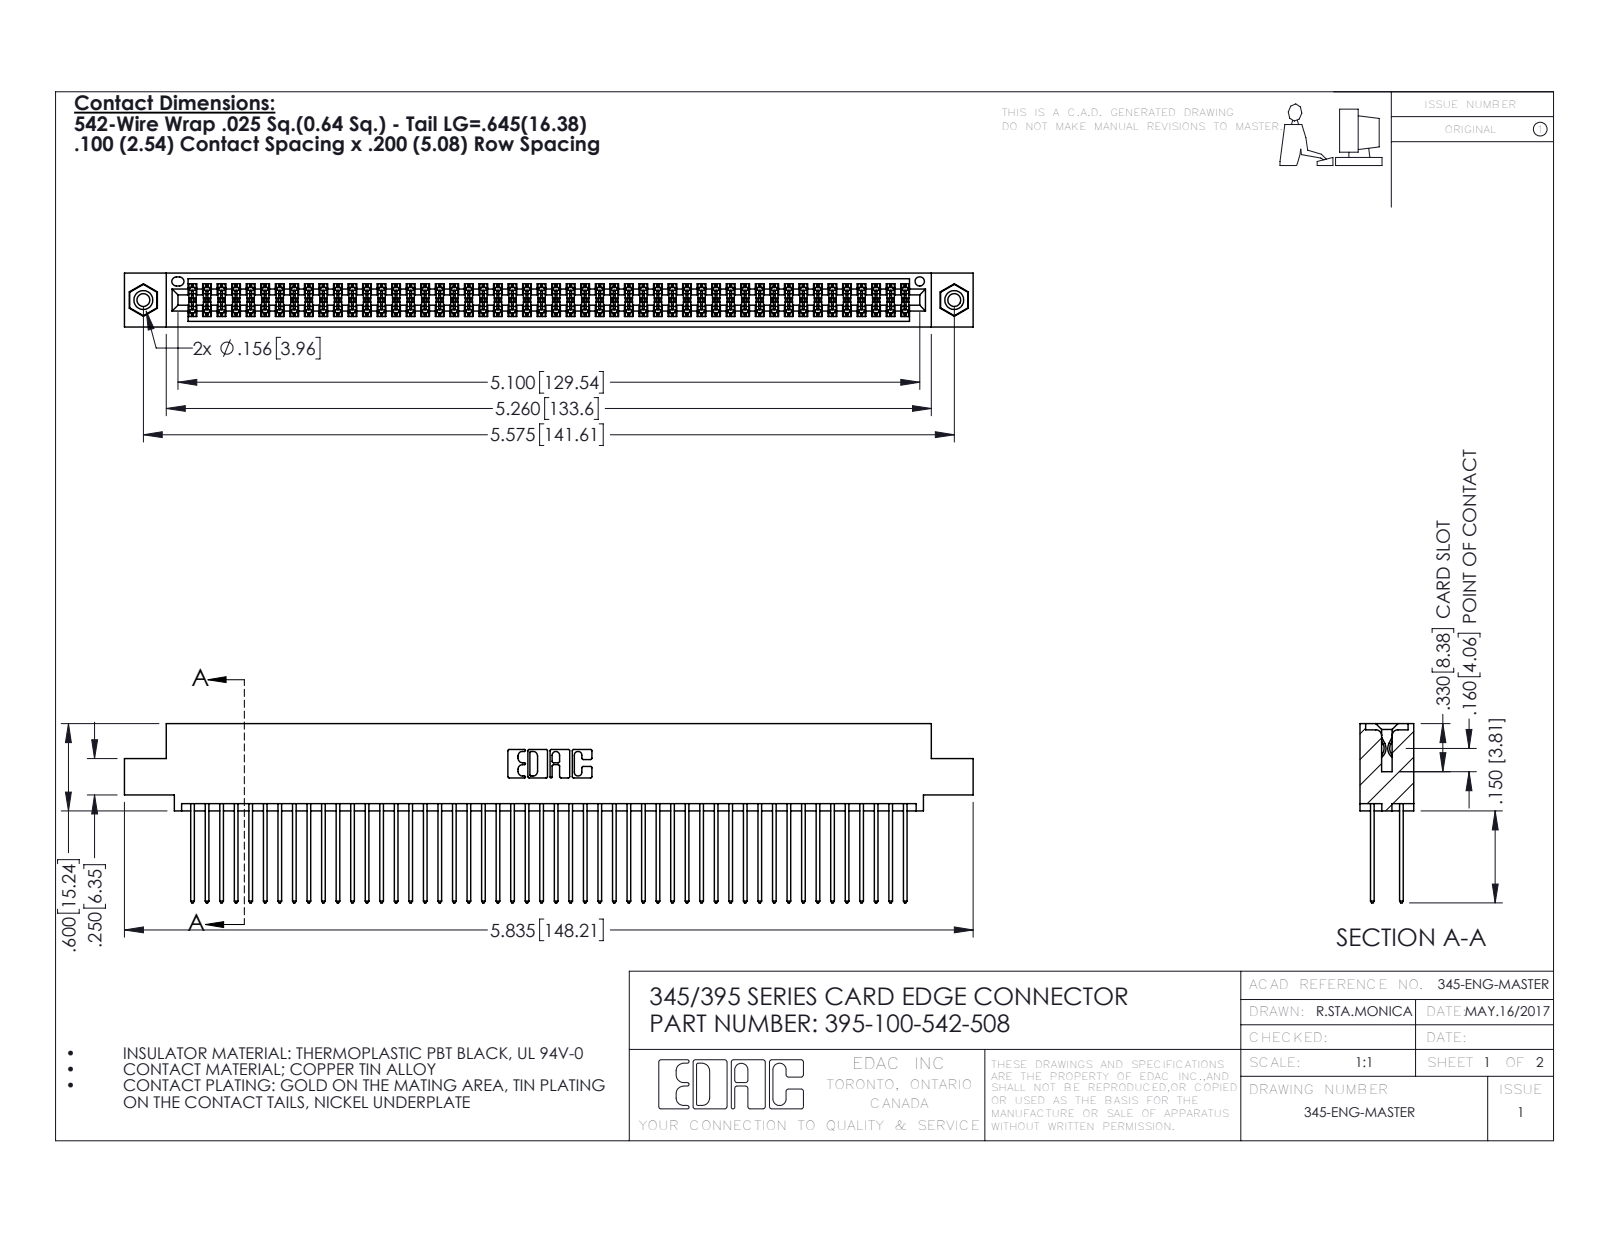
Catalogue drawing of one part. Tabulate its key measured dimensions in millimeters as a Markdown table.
| quantity | value |
| --- | --- |
| part name | 345-292-001_345-293-142; 345 Part_0.110 Offset - 0.156 Dia-TI; 395-100-542-508; 345-250-001_345-250-003-102 |
| STEP written by | SolidWorks 2016 (CONFIG_CONTROL_DESIGN) |
| units | millimeters |
| bodies | 103 solids, 5190 faces (3416 planar, 1758 cylindrical, 16 other) |
| overall size | 148.2 × 31.3 × 9.4 |
| volume | 14 900 mm³ |
| surface area | 24 400 mm² |
| round holes (diameter × count) | 2.3 × 2, 3.2 × 2, 4 × 2, 1.6 × 1 |
| round bosses / shafts (diameter × count) | 3.9 × 2 |
| partial cylindrical surfaces (radius × count) | 0.2 × 150, 0.3 × 100, 0.3 × 22, 0.2 × 6, 0.8 × 6, 0.7 × 3, 0.4 × 2, 0.5 × 2 |
| main face-to-face distances | 1.8, 7.6, 5.1, 2.5, 6.9, 0.6, 5.7, 9.4, 4.4, 3.8 |
| hole center spacings | 6.9, 135.6, 141.6 |
